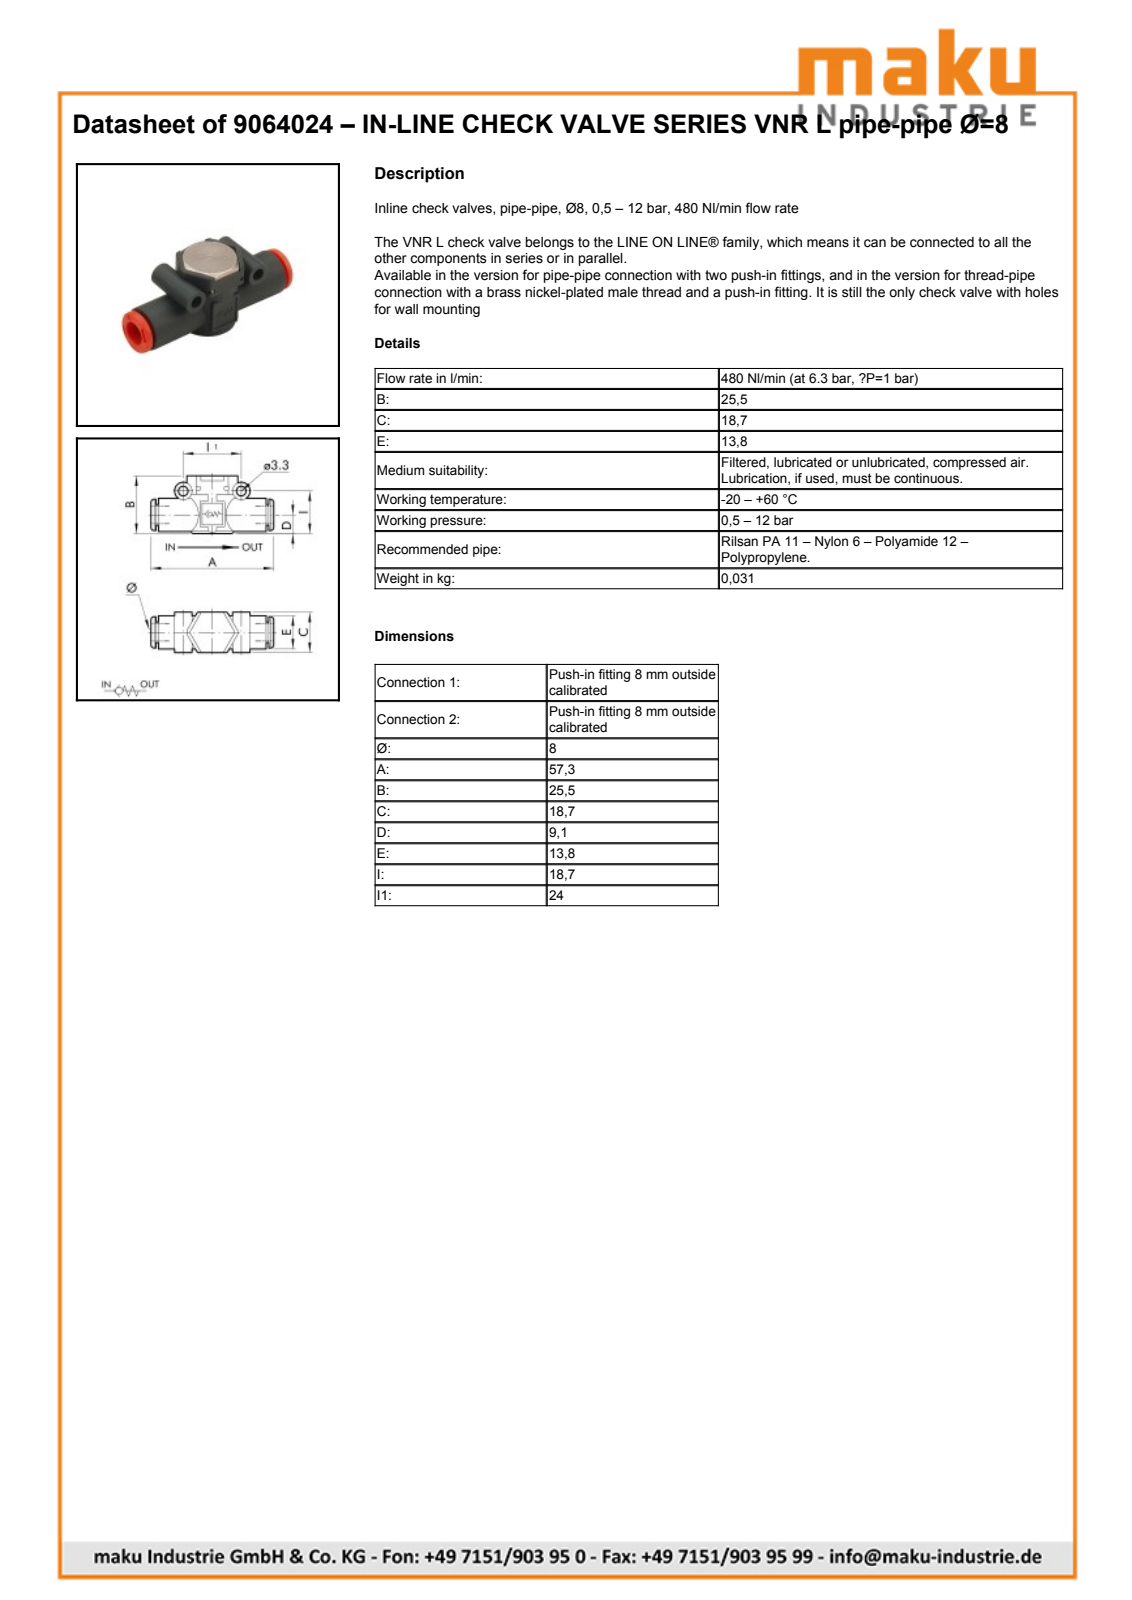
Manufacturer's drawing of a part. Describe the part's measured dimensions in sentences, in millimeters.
The part is named "9064024; LINE-ON-LINE D8 VSR-L body; LINE-ON-LINE D8 VNR-L bushing; LINE ON LINE D8 VNR-L plate". Its 3-D file was written by "PARTsolutions (AUTOMOTIVE_DESIGN)". It is 4 solids with 148 faces: 95 planar, 46 cylindrical and 7 other. Overall it measures 57.2 by 26 by 18.7 millimeters. Its volume is 7 356 cubic millimeters and its surface area 9 326 square millimeters. Round holes: 2 of diameter 3.3, 2 of diameter 6, 1 of diameter 5.5, 1 of diameter 8.1, 1 of diameter 9.4, 1 of diameter 11, 1 of diameter 11.66, 1 of diameter 12.5, 1 of diameter 15. Round bosses or shafts: 2 of diameter 6, 1 of diameter 18.8, 1 of diameter 13.8, 1 of diameter 13.6, 1 of diameter 9.5, 1 of diameter 9.2. Partial cylindrical surfaces (rounded edges, fillets, slot ends): 1 of radius 3.75, 1 of radius 10.2, 1 of radius 10.35, 1 of radius 11.45. The main face-to-face distances are 1.9, 24.1, 26, 0.94, 49.06, 4.1, 20, 21.9, 1.7, 2.64. The hole center spacings are 15.37, 24.
